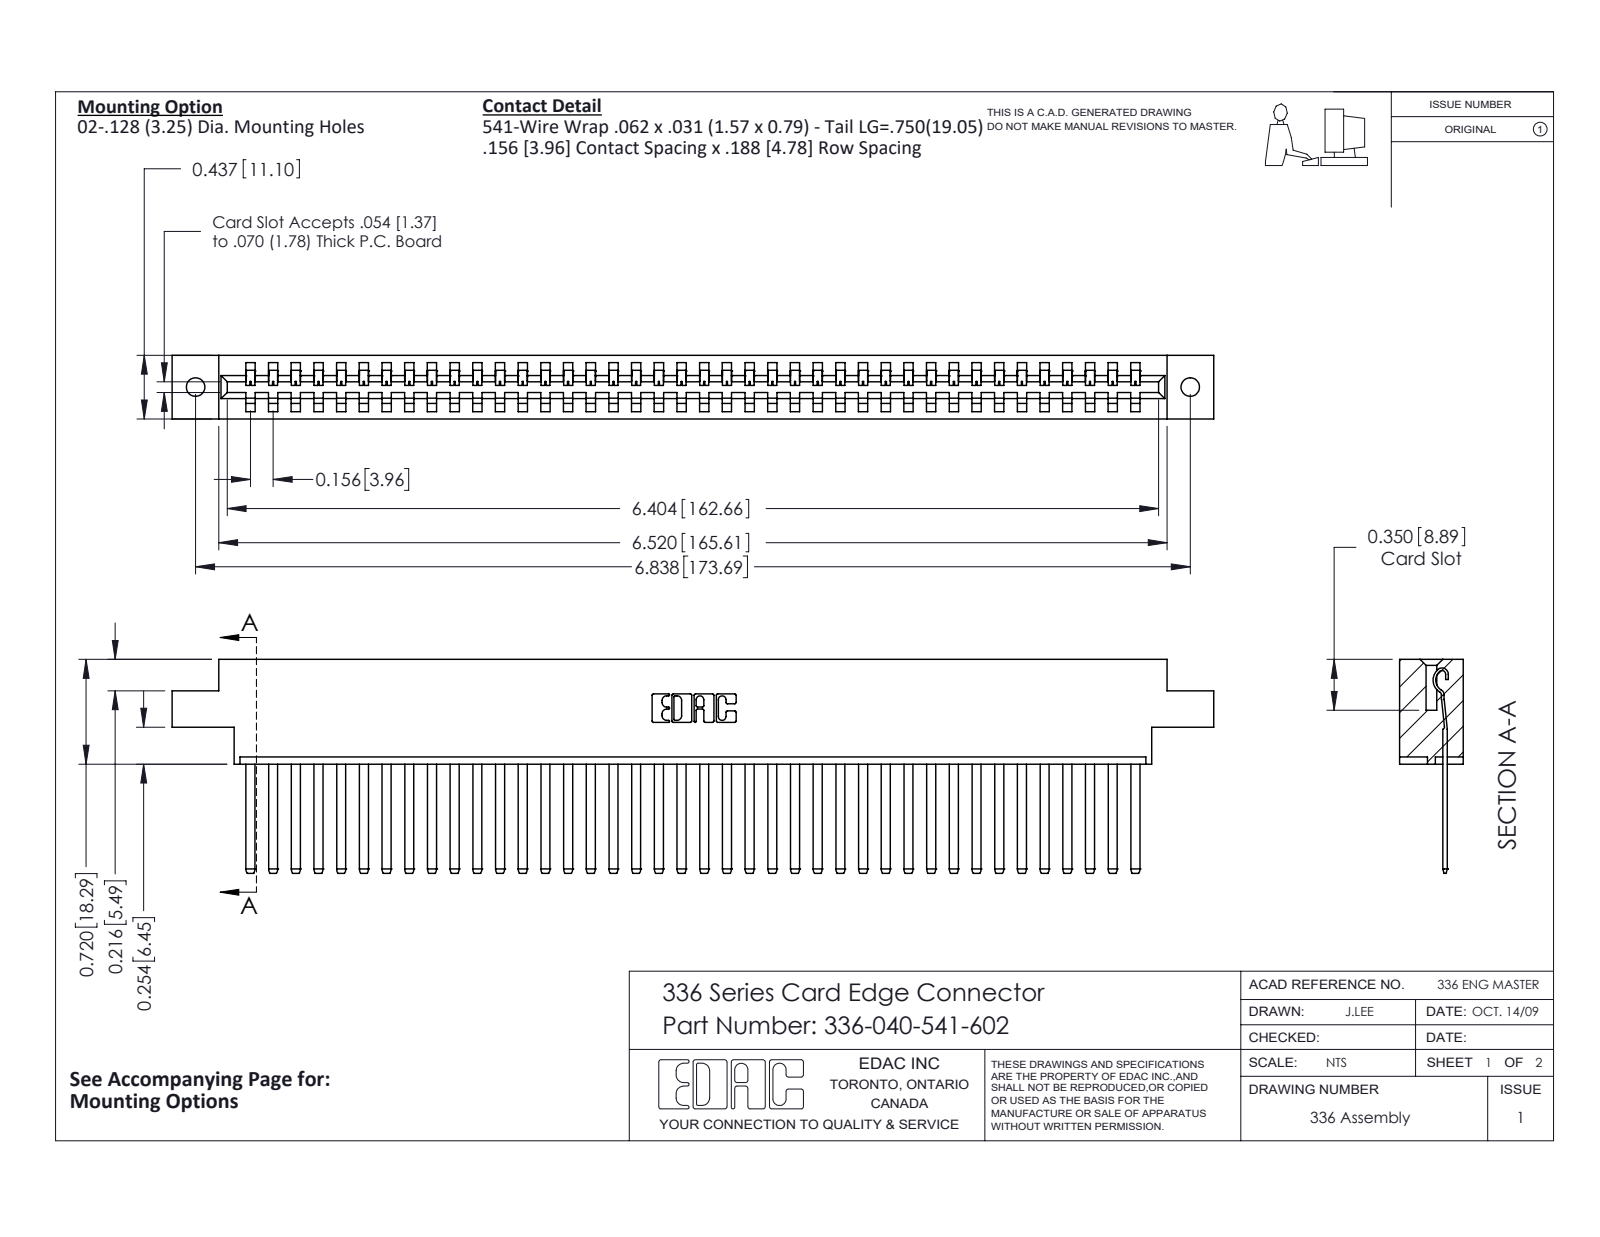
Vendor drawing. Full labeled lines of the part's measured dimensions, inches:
Part name (STEP PRODUCT): 336 Part_Offset - .128 Dia; 336-290-001_336-290-541; 336-040-541-602
STEP written by: SolidWorks 2020 (CONFIG_CONTROL_DESIGN)
Units: inches
Bodies: 41 solids, 2118 faces (1434 planar, 684 cylindrical, 0 other)
Overall size (bounding box): 7.161 × 1.47 × 0.437
Volume: 1.603 in³ · Surface area: 44.14 in²
Round holes (diameter × count): ⌀0.128 ×2
Partial cylindrical surfaces — rounded edges, fillets, slot ends (radius × count): R0.004 ×80, R0.056 ×80, R0.01 ×22, R0.007 ×6, R0.031 ×6, R0.026 ×3, R0.022 ×2, R0.04 ×2
Main face-to-face distances: 0.437, 0.181, 0.328, 0.14, 0.297, 0.109, 0.031, 0.256, 0.05, 0.387
Hole centre spacings: 6.838
